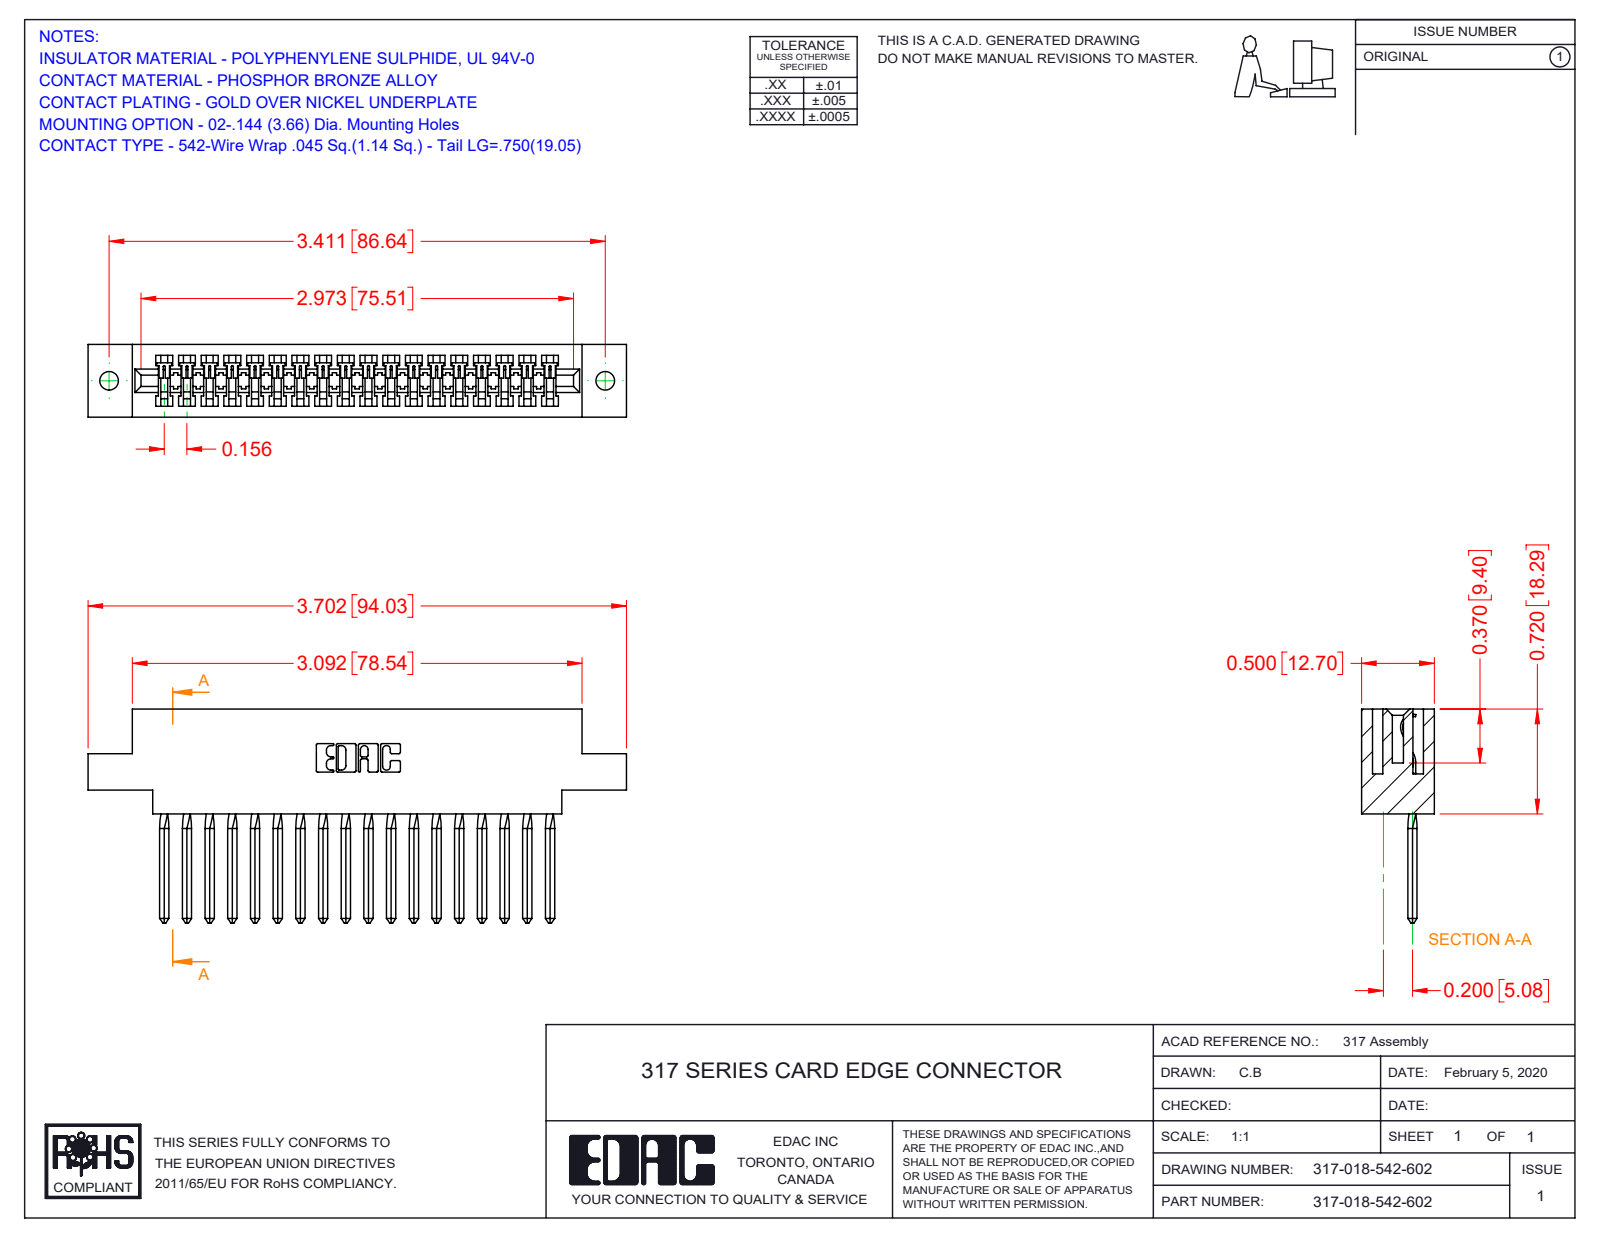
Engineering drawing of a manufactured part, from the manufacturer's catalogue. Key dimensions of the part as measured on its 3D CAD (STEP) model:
Part name (STEP PRODUCT): 317-018-542-602; 317-290-003_542; 317 Part_.144 Dia
STEP written by: SolidWorks 2016 (CONFIG_CONTROL_DESIGN)
Units: inches
Bodies: 19 solids, 1452 faces (1210 planar, 170 cylindrical, 72 other)
Overall size (bounding box): 3.702 × 1.47 × 0.5
Volume: 0.845 in³ · Surface area: 24.94 in²
Round holes (diameter × count): ⌀0.128 ×2
Partial cylindrical surfaces — rounded edges, fillets, slot ends (radius × count): R0.006 ×36, R0.01 ×22, R0.007 ×6, R0.031 ×6, R0.026 ×3, R0.074 ×1, R0.089 ×1, R0.1 ×1
Main face-to-face distances: 0.5, 0.075, 0.425, 0.11, 0.35, 0.136, 0.72, 0.065, 0.211, 0.289
Hole centre spacings: 3.411
